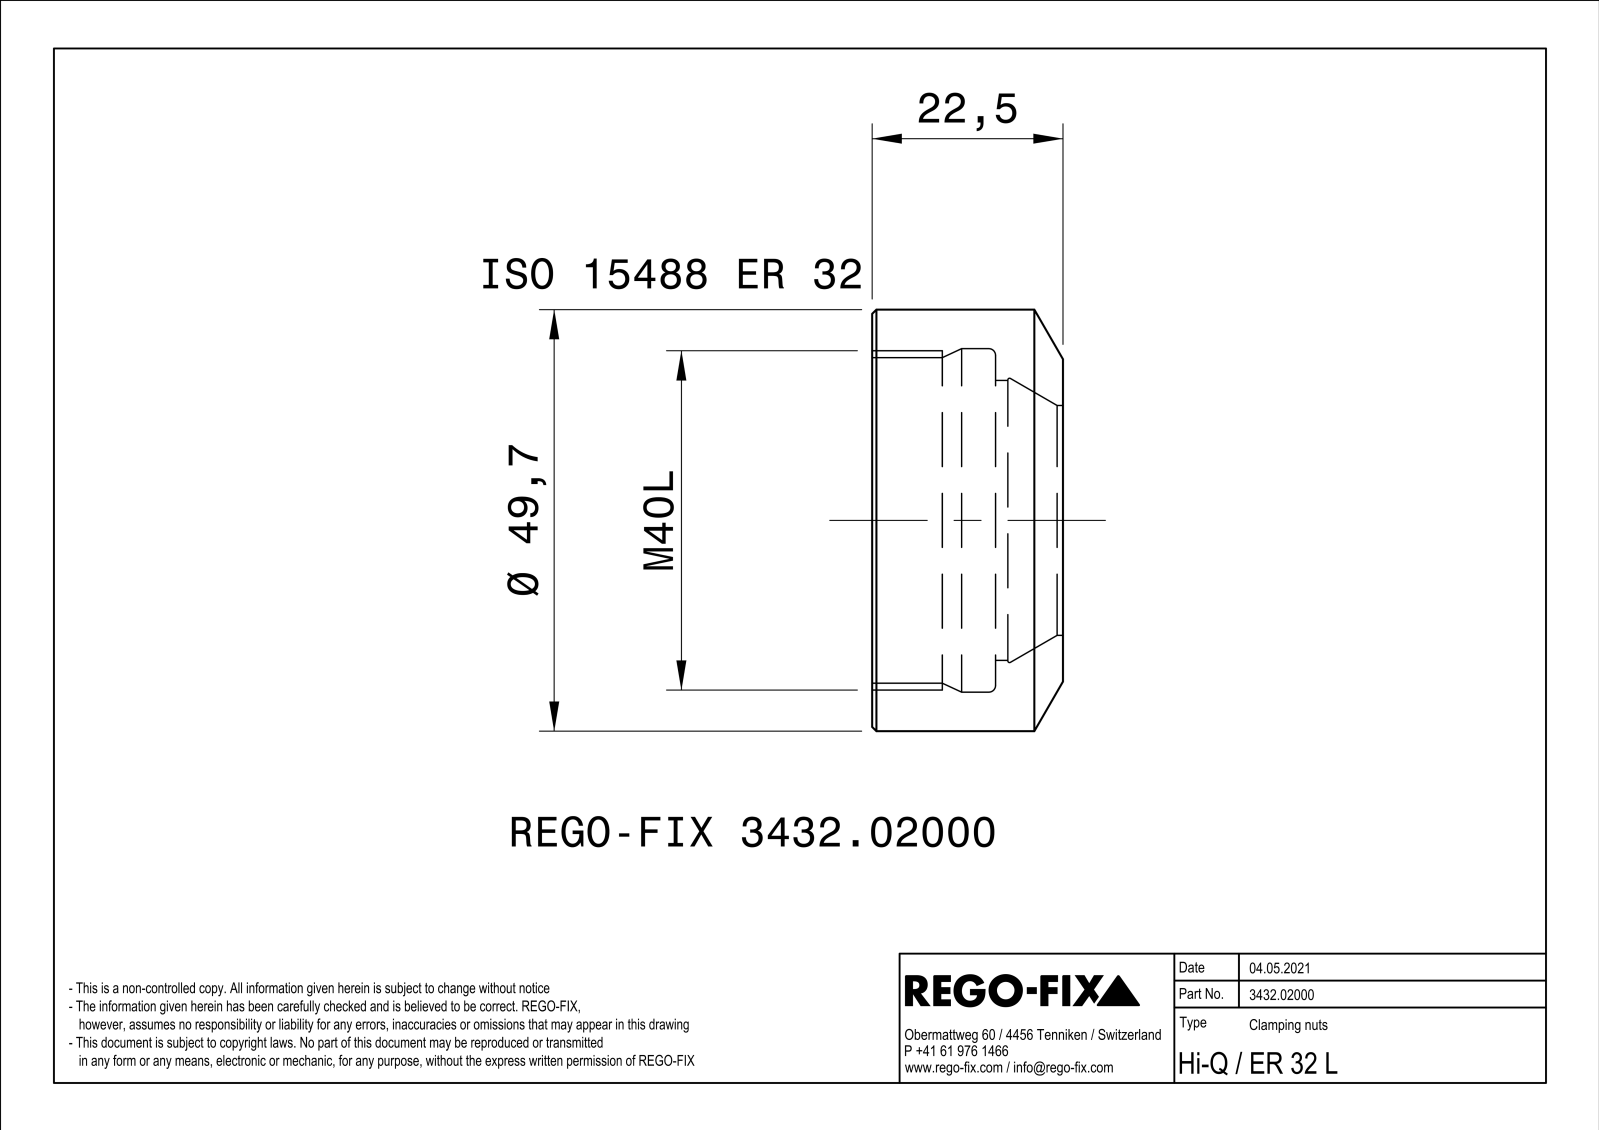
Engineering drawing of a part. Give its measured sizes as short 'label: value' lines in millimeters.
name: NOCUT
written by: SIEMENS PLM Software Solid Edge ST10 (AUTOMOTIVE_DESIGN)
unit: mm
bodies: 1 solid, 81 faces (46 planar, 5 cylindrical, 30 other)
size: 49.7 × 49.7 × 22.5
volume: 17 917 mm³; area: 8 474 mm²
holes: 1× ⌀27.1, 1× ⌀33, 1× ⌀38.38, 1× ⌀40.5
bosses: 1× ⌀49.7
face distances: 22.5, 7.95, 14.55, 44, 6.94, 6.96, 36.46, 32.58, 32.56, 32.6
